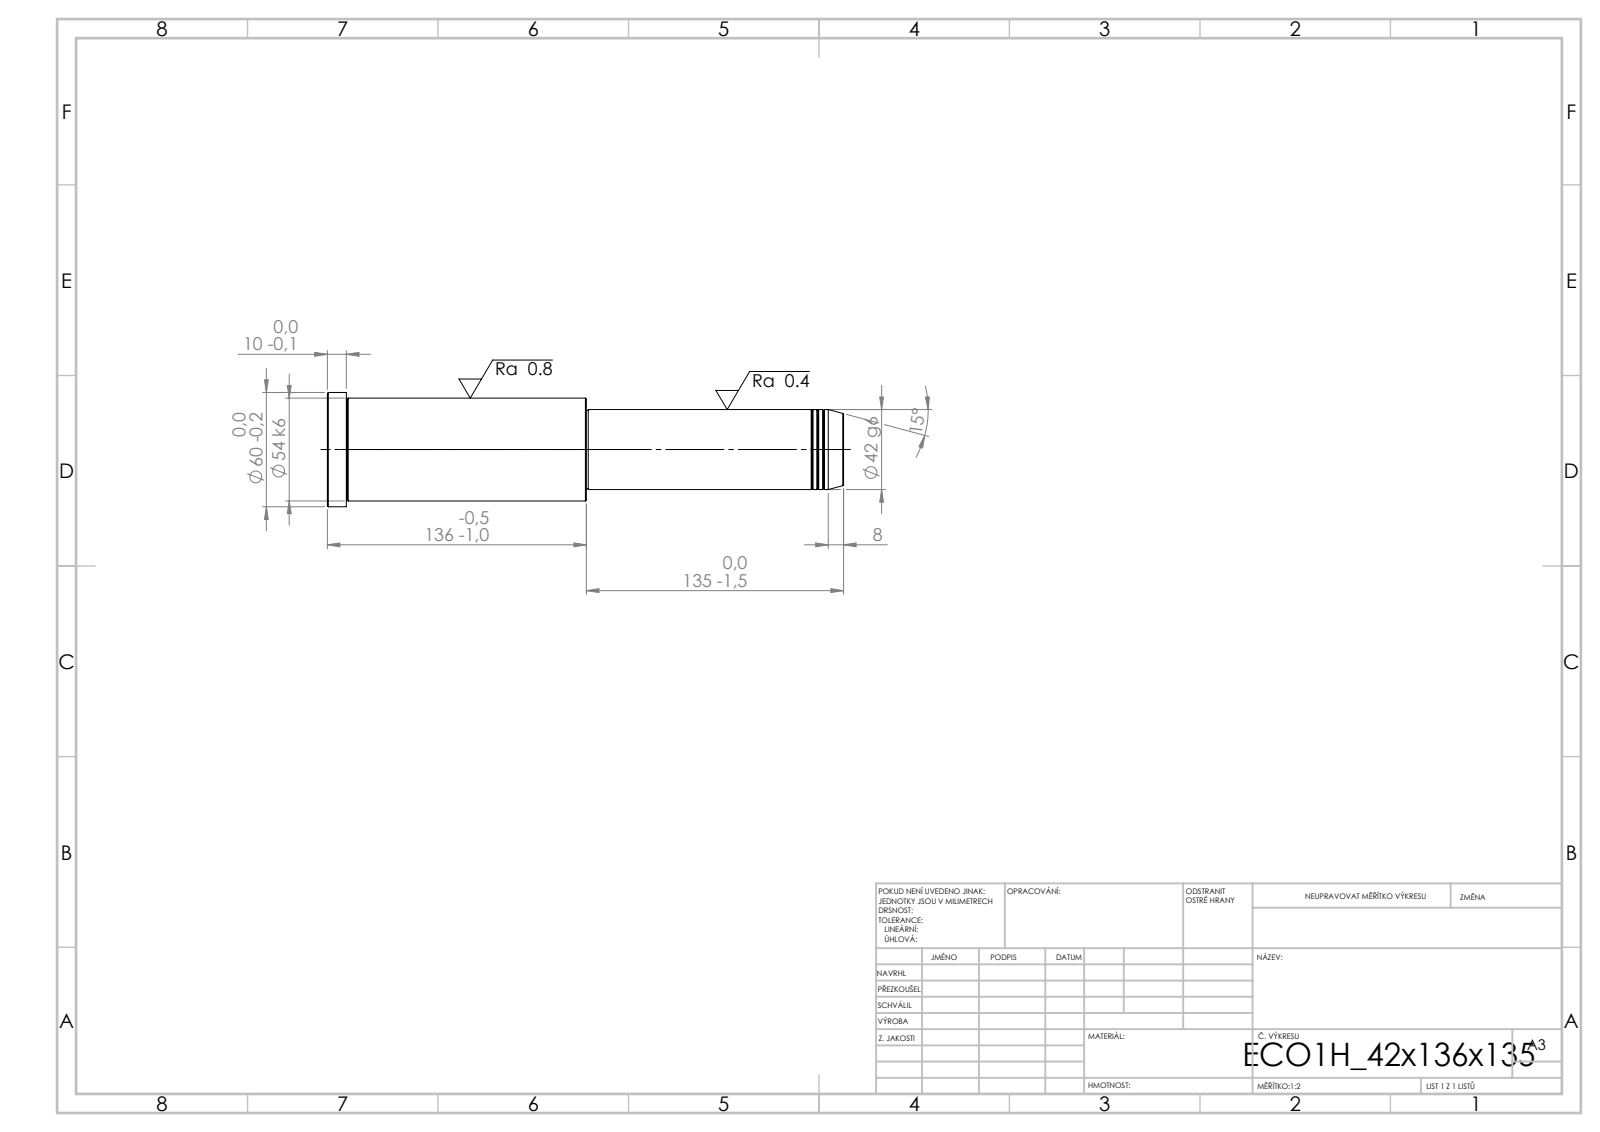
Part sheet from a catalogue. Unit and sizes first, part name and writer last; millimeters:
Units: millimetres
Overall size (bounding box): 271 × 60 × 60
Round bosses / shafts (diameter × count): ⌀60 ×1, ⌀54 ×1, ⌀42 ×1, ⌀41 ×1
Main face-to-face distances: 271, 135, 136, 261, 126, 10, 134, 1, 127, 137
Volume: 502 451 mm³ · Surface area: 46 760 mm²
Bodies: 1 solid, 43 faces (5 planar, 14 cylindrical, 24 other)
STEP written by: SolidWorks 2019 (CONFIG_CONTROL_DESIGN)
